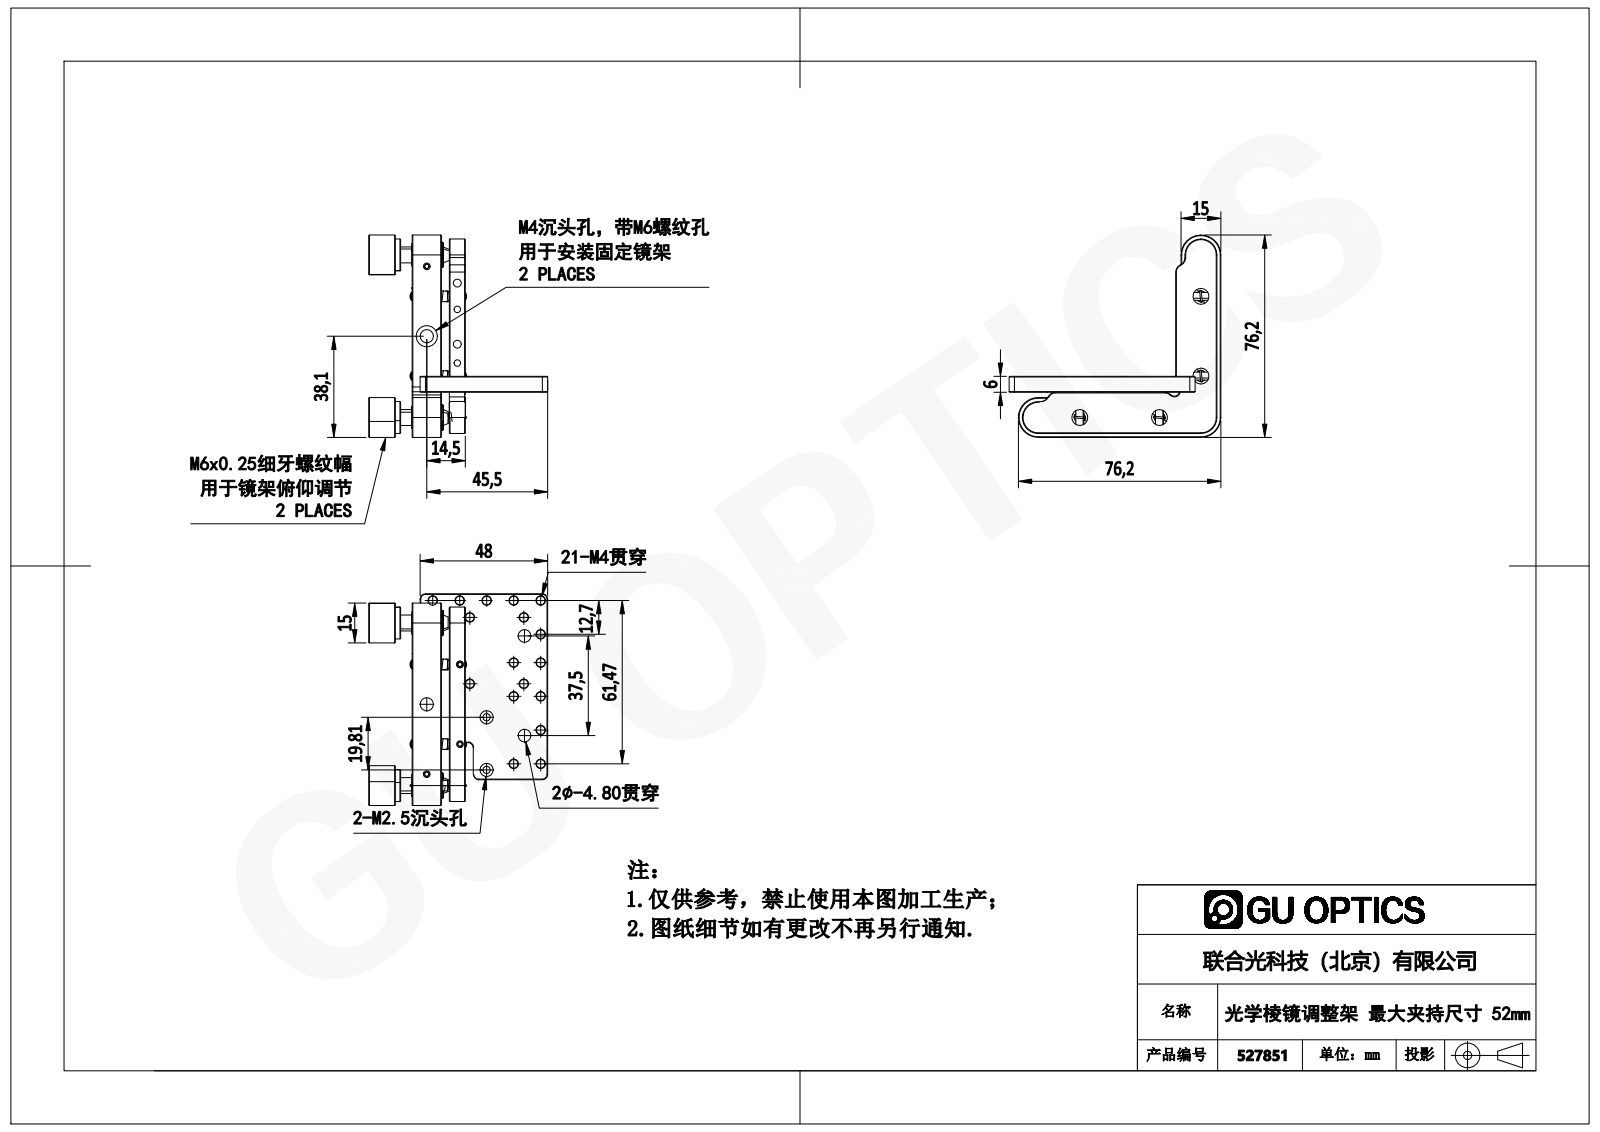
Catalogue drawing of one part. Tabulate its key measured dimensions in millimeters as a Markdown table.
| quantity | value |
| --- | --- |
| part name | 527851 |
| STEP written by | SolidWorks 2020 (CONFIG_CONTROL_DESIGN) |
| units | millimeters |
| bodies | 0 solids, 423 faces (199 planar, 121 cylindrical, 103 other) |
| overall size | 79.7 × 76.2 × 67.44 |
| round holes (diameter × count) | 6.5 × 4, 9.5 × 3, 5 × 2, 8 × 2, 2.3 × 1, 8.6 × 1 |
| round bosses / shafts (diameter × count) | 3.3 × 22, 3 × 9, 6 × 8, 4 × 6, 1.5 × 6, 1.6 × 4, 2.8 × 3, 15 × 2 |
| partial cylindrical surfaces (radius × count) | 2 × 12, 3 × 9, 0.8 × 8, 6 × 3, 7.5 × 1 |
| main face-to-face distances | 6, 3, 9, 11, 20, 14, 15, 17, 1.5, 2 |
| hole center spacings | 15.6, 45.6, 30, 48.19, 61.2, 63.16, 76.32, 22.06 |
